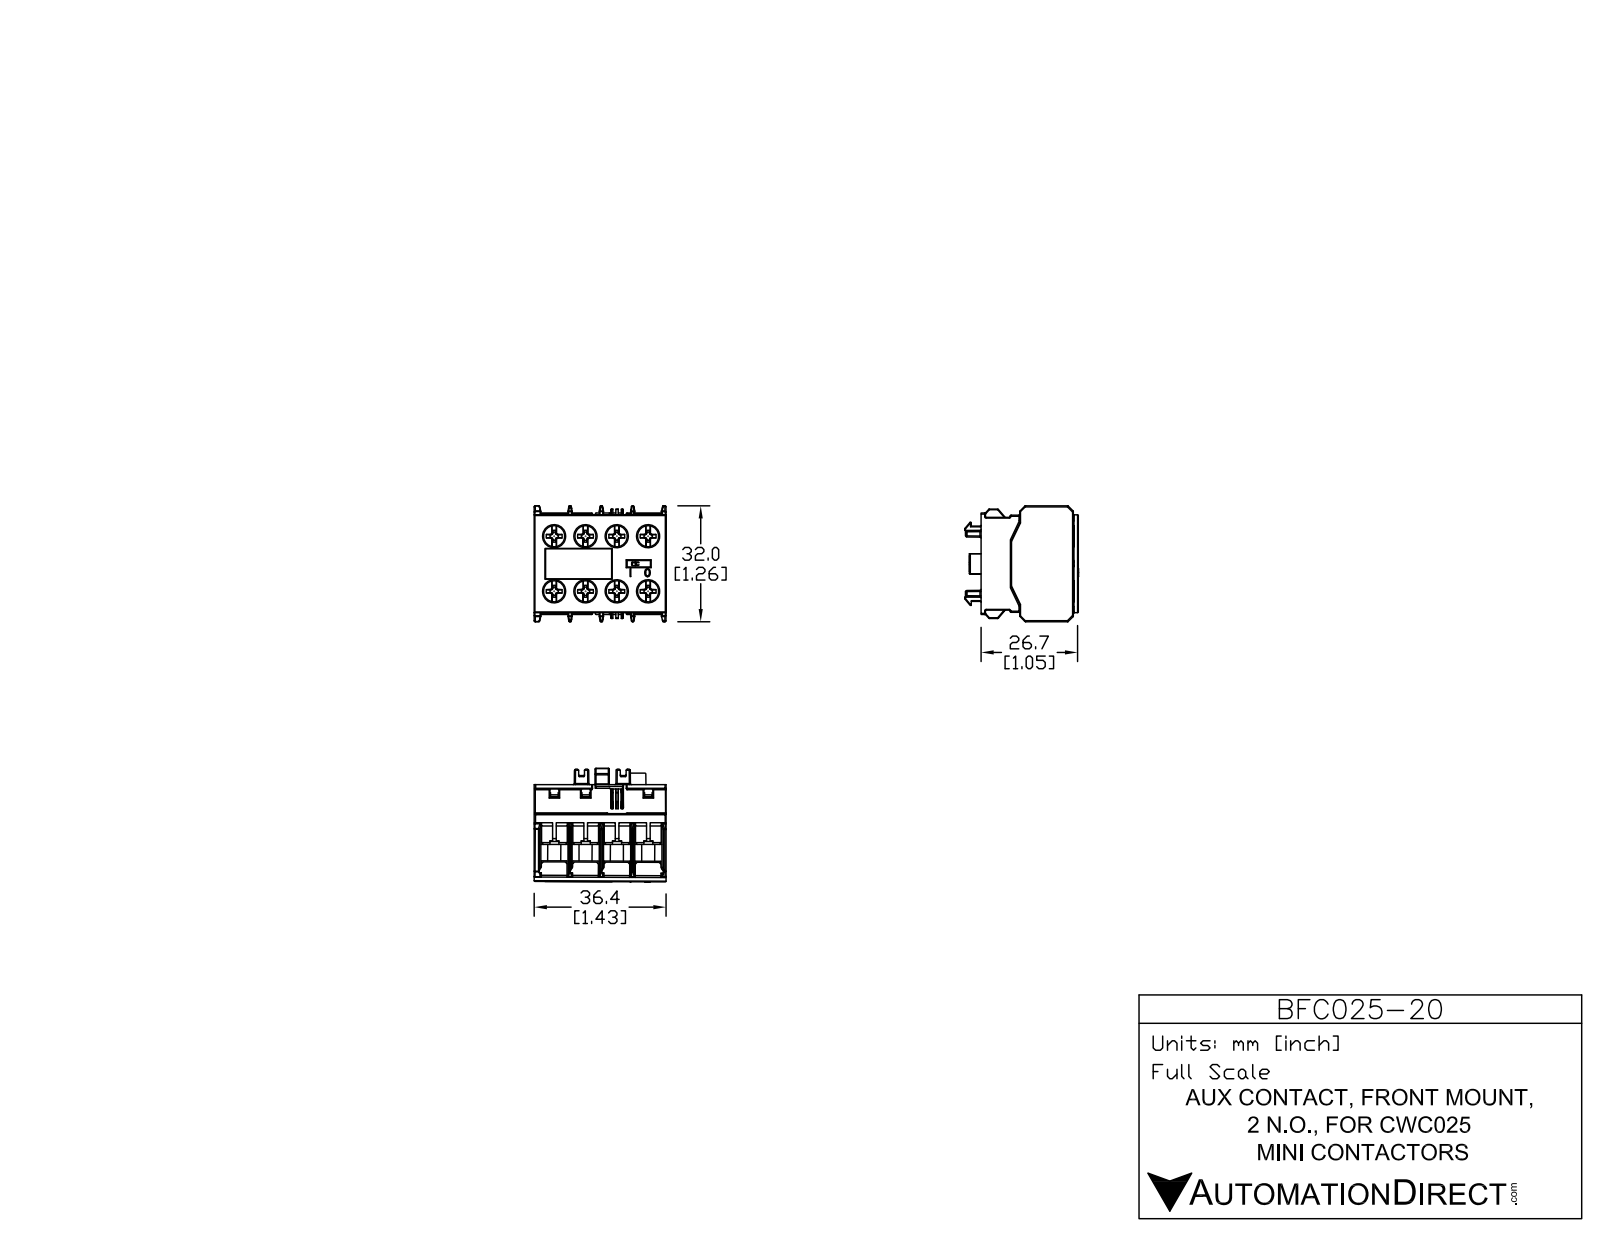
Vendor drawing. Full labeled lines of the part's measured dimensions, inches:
Part name (STEP PRODUCT): BFC025-20
STEP written by: SolidWorks 2013 (AUTOMOTIVE_DESIGN)
Units: inches
Bodies: 24 solids, 1105 faces (763 planar, 278 cylindrical, 64 other)
Overall size (bounding box): 1.437 × 1.26 × 1.249
Volume: 1.6 in³ · Surface area: 37.1 in²
Round holes (diameter × count): ⌀0.236 ×8
Round bosses / shafts (diameter × count): ⌀0.197 ×8, ⌀0.118 ×8
Partial cylindrical surfaces — rounded edges, fillets, slot ends (radius × count): R0.008 ×58, R0.02 ×8, R0.178 ×8, R0.012 ×6, R0.01 ×4, R0.006 ×2, R0.007 ×2
Main face-to-face distances: 0.049, 0.34, 0.679, 0.339, 0.63, 0.389, 0.291, 0.314, 1.019, 1.437
Hole centre spacings: 0.34, 0.591, 0.679, 0.681, 0.9, 0.339, 0.681, 1.019
